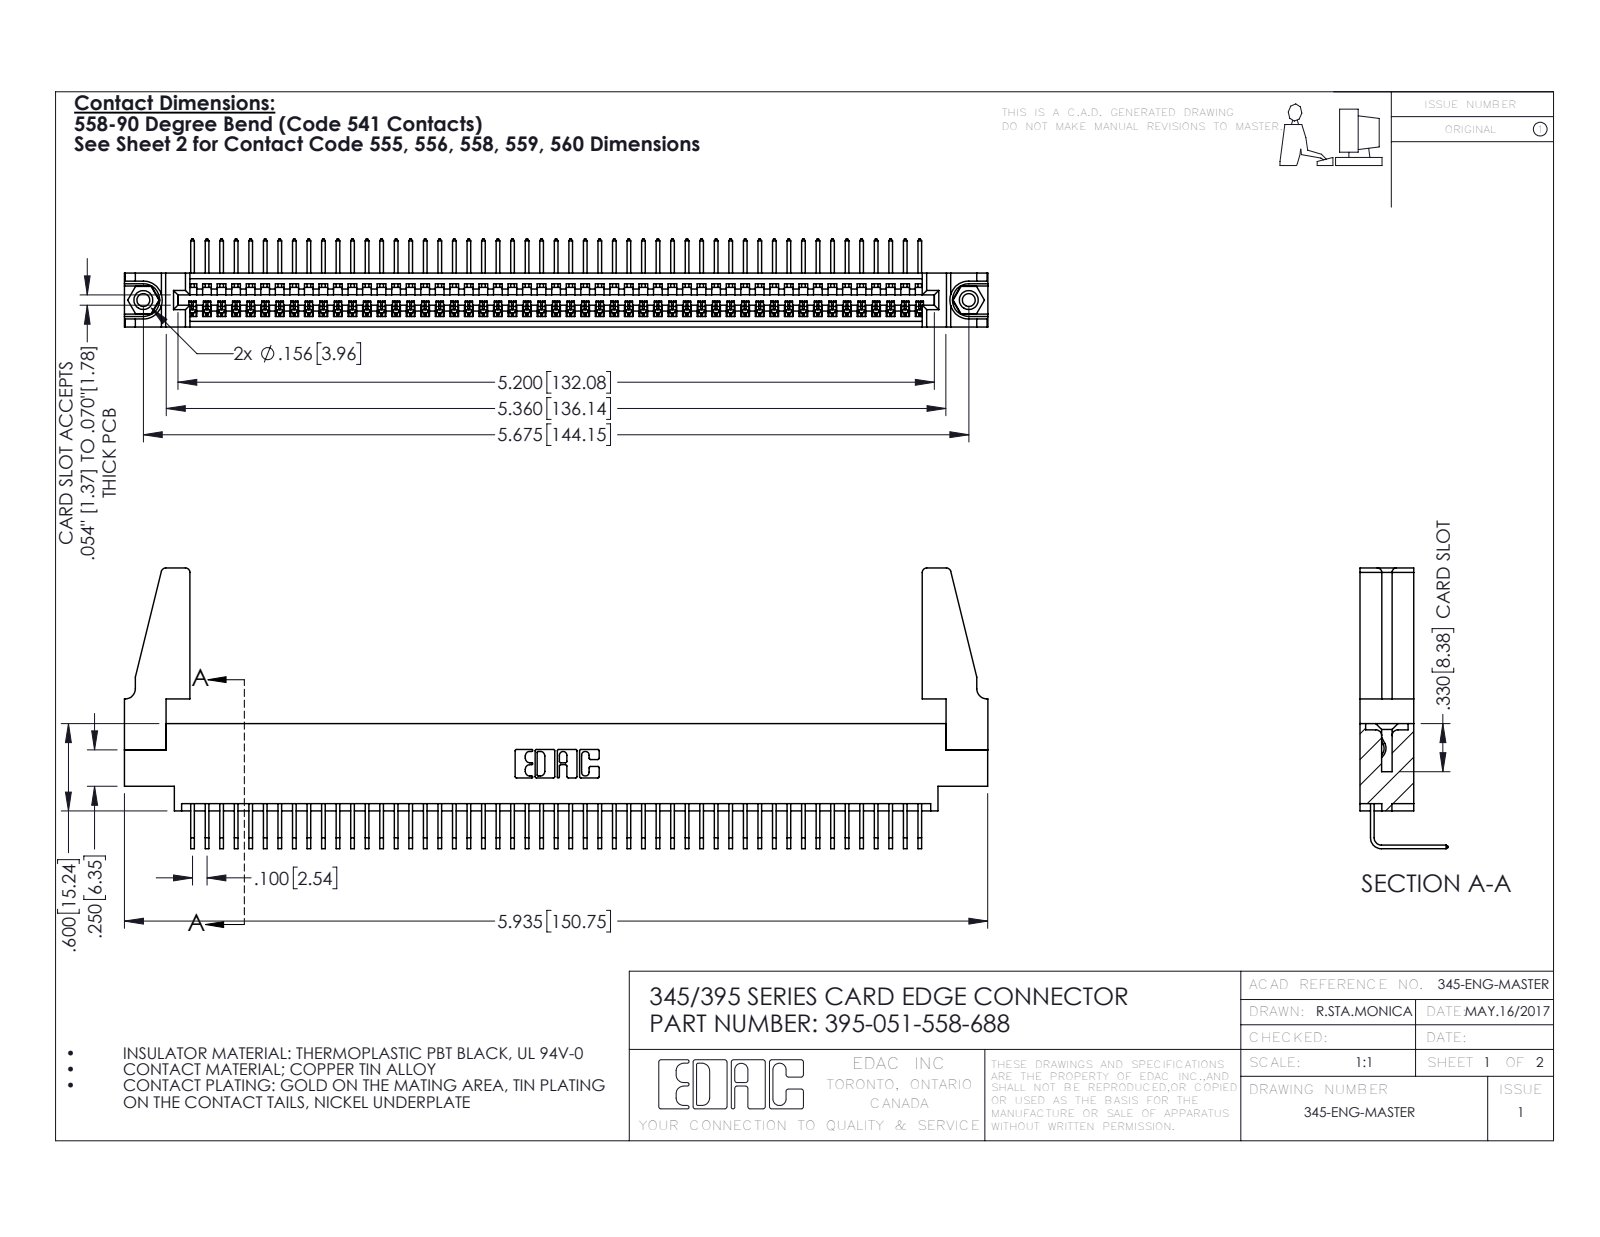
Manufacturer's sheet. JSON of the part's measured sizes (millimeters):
{"part_name": "345-220-078_345-220-088; 345-250-001_345-250-001-102; 345 Part_0.170 Offset - 0.156 Dia-TH; 395-051-558-688 (+1 more)", "step_written_by": "SolidWorks 2016 (CONFIG_CONTROL_DESIGN)", "units": "millimeters", "bodies": {"solids": 56, "faces": 3314, "planar": 2298, "cylindrical": 1000, "other": 16}, "overall_size": [150.8, 49, 15.4], "volume_mm3": 17700, "surface_area_mm2": 23580, "round_holes": [[2.3, 2], [3.2, 2], [4, 2], [1.6, 1]], "round_bosses_or_shafts": [[3.9, 2]], "partial_cylinders_radius": [[0.2, 102], [0.3, 22], [0.8, 8], [0.2, 6], [0.8, 6], [0.7, 3], [0.8, 2], [1, 2]], "face_to_face_distances": [1.8, 7.6, 9.4, 5.1, 2.5, 6.9, 0.6, 5.7, 4.4, 3.8], "hole_center_spacings": [6.9, 138.2, 144.1]}
